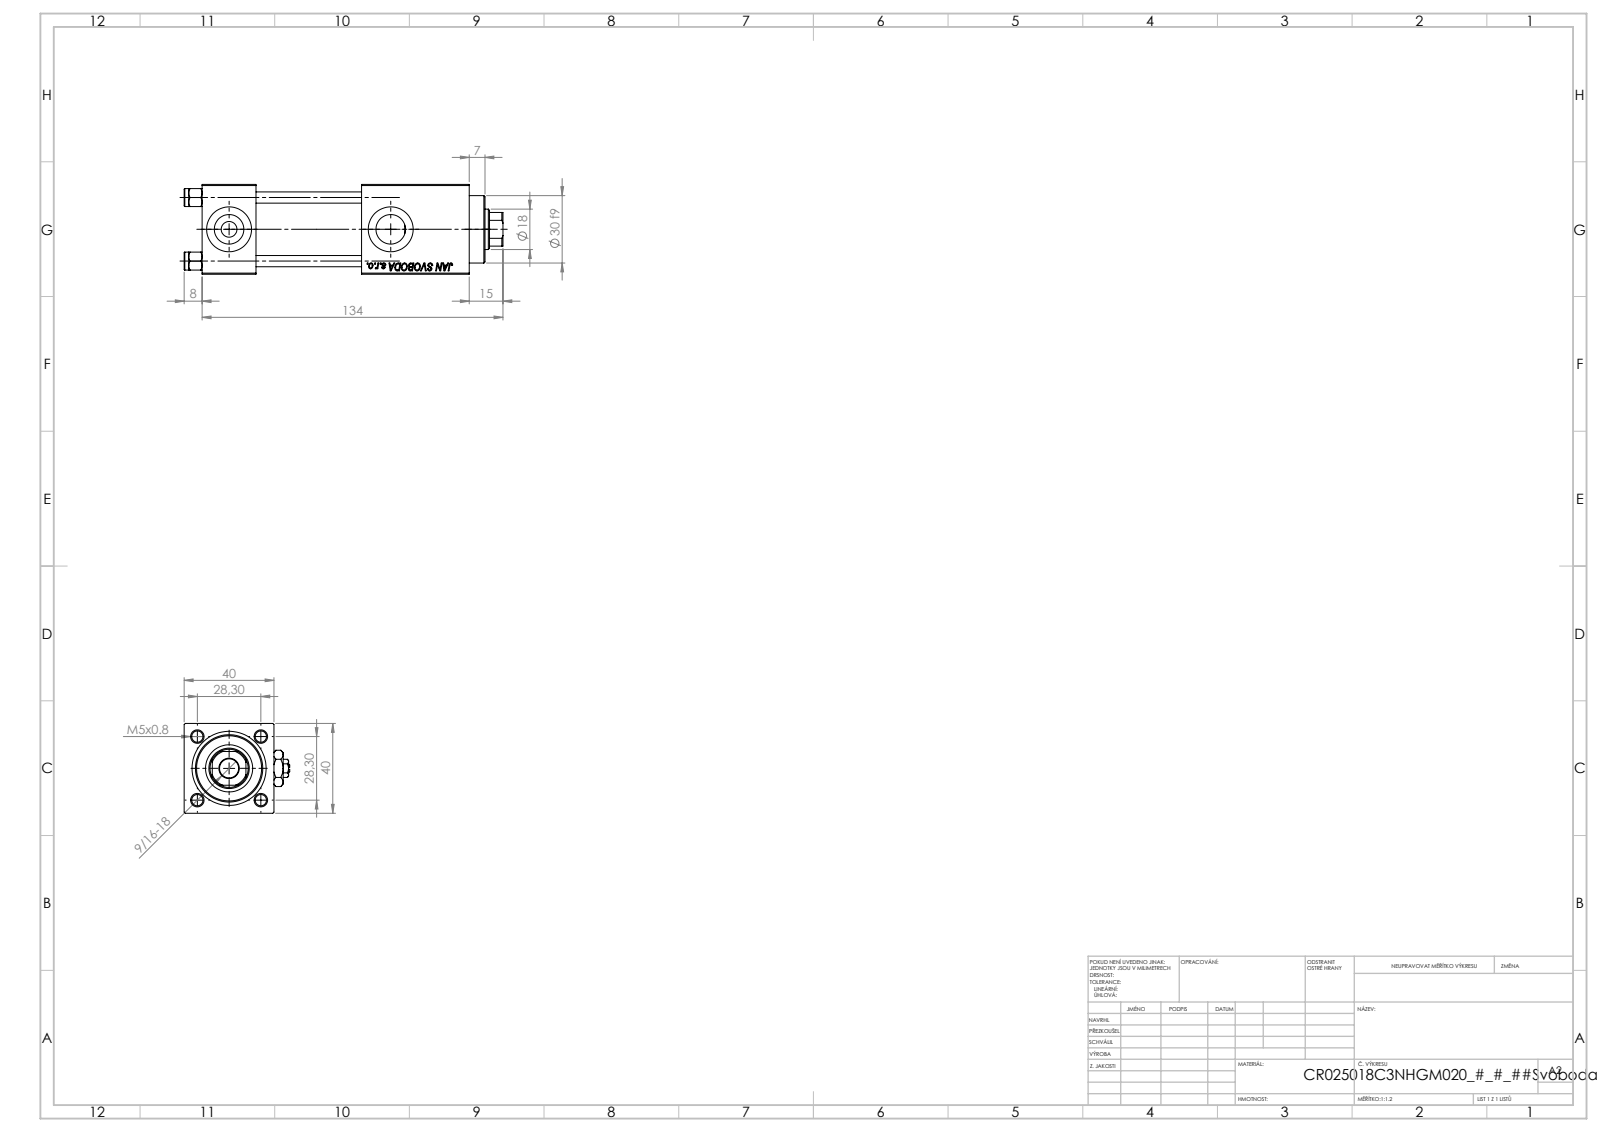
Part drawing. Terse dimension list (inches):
name: V215_VC_A; NUT_M5_C; V215CR_C_Body; Zatka_pro_OIL_PORT (+2 more)
written by: SolidWorks 2019 (CONFIG_CONTROL_DESIGN)
unit: in
bodies: 13 solids, 1245 faces (571 planar, 96 cylindrical, 578 other)
size: 5.591 × 1.85 × 1.575
volume: 9.068 in³; area: 90.65 in²
holes: 4× ⌀0.197, 3× ⌀0.787, 2× ⌀0.276, 2× ⌀0.518, 1× ⌀0.335, 1× ⌀0.709, 1× ⌀0.827, 1× ⌀0.984, 1× ⌀1.181
bosses: 4× ⌀0.315, 1× ⌀1.22
rounds: 1× R0.335
face distances: 1.575, 0.945, 1.567, 1.85, 2.795, 3.555, 2.61, 0.76, 1.89, 4.685
hole spacings: 0.788, 1.114, 1.576, 2.835
